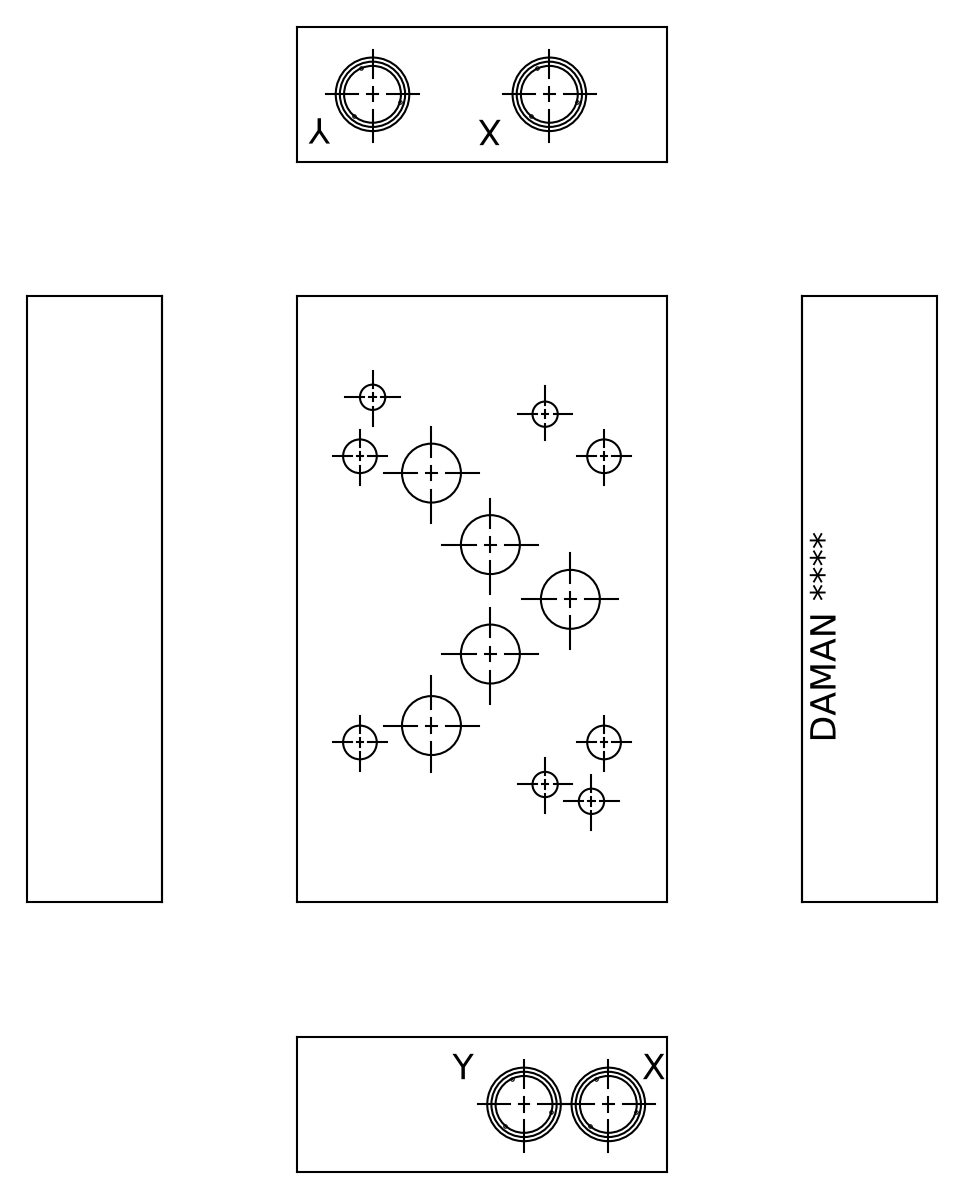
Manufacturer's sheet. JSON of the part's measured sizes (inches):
{"part_name": "Part_AD05HTPXY4P.C02765R6_3D", "step_written_by": "Autodesk Inventor 2022 (AUTOMOTIVE_DESIGN)", "units": "inches", "bodies": {"solids": 1, "faces": 414, "planar": 317, "cylindrical": 30, "other": 67}, "overall_size": [4.5, 2.75, 1], "volume_in3": 10.42, "surface_area_in2": 54.71, "round_holes": [[0.438, 6], [0.625, 6], [0.187, 4], [0.281, 4], [0.422, 4], [0.546, 4]], "partial_cylinders_radius": [[0.219, 1], [0.313, 1]], "face_to_face_distances": [1, 2.75, 4.5, 0.052, 0.948, 0.625, 3.875, 3.25, 2.748, 0.624], "hole_center_spacings": [0.447, 0.537, 0.547, 0.689, 0.719, 0.95, 1.069, 1.092]}
